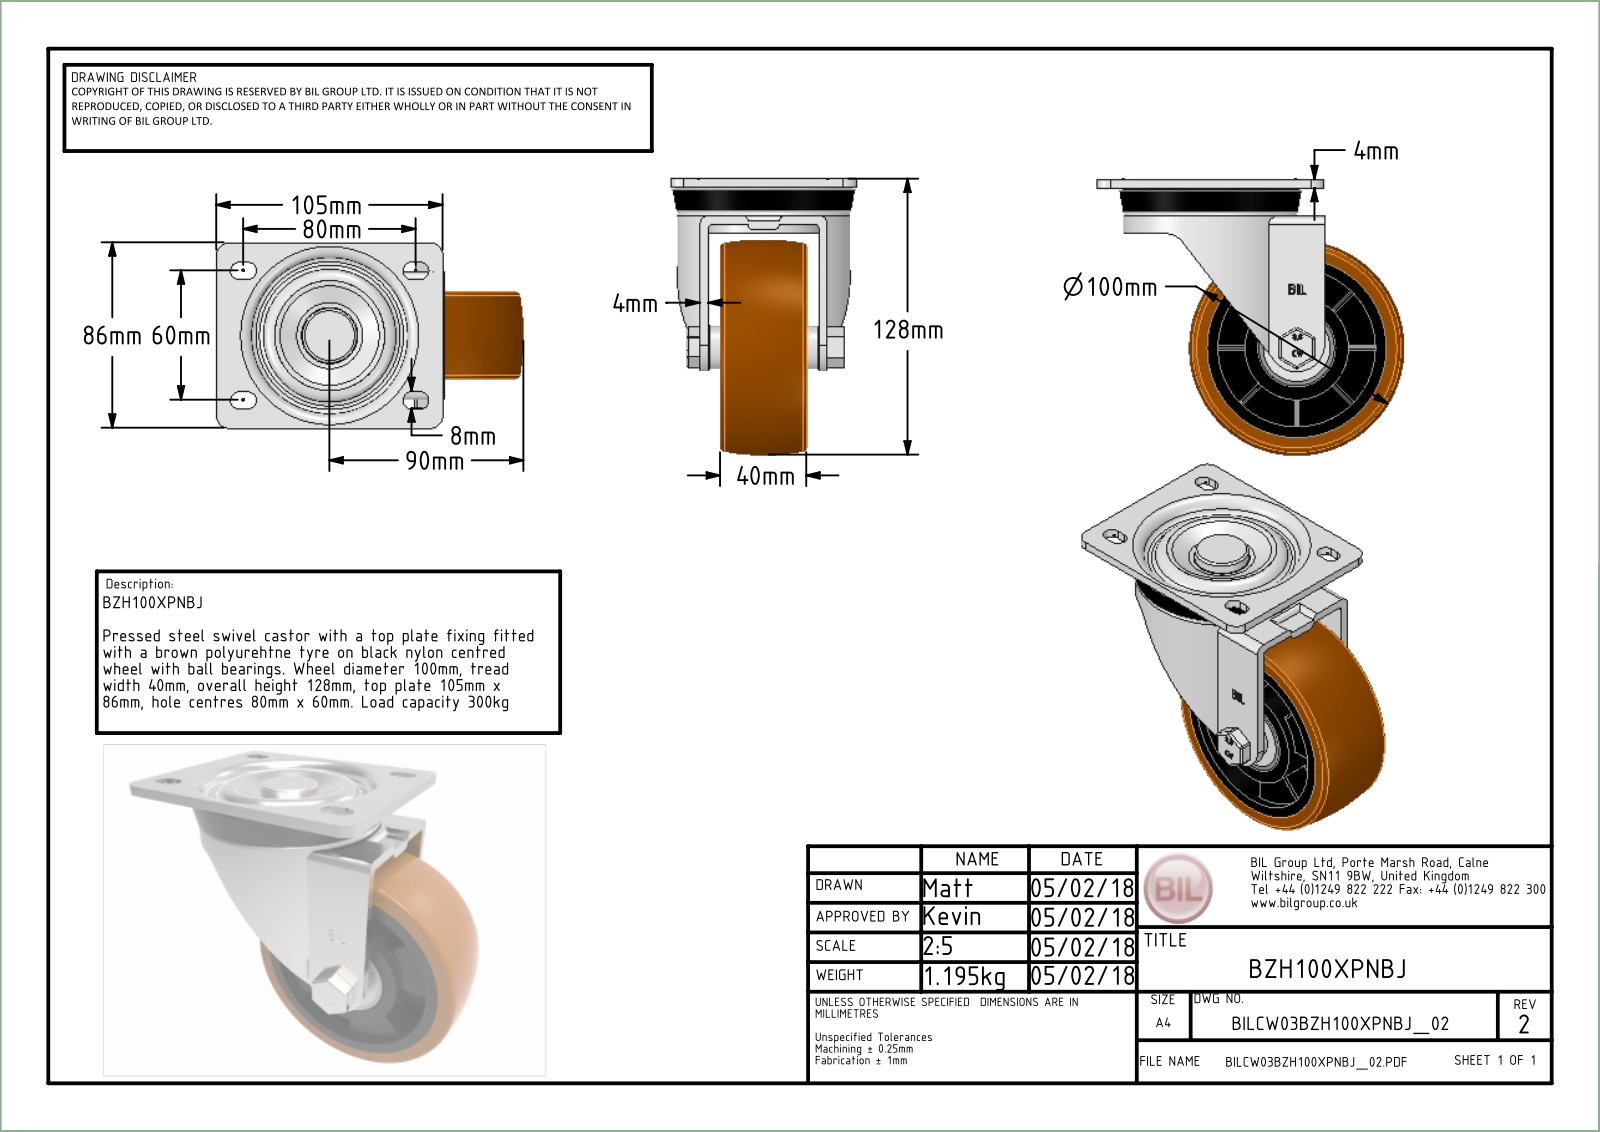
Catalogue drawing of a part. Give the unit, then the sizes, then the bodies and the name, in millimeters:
Units: millimetres
Overall size (bounding box): 142.5 × 128 × 86
Round holes (diameter × count): ⌀32 ×2, ⌀10 ×1, ⌀10.2 ×1, ⌀10.5 ×1, ⌀12 ×1, ⌀15 ×1, ⌀22.5 ×1, ⌀25 ×1, ⌀30 ×1, ⌀31 ×1, ⌀35 ×1, ⌀72 ×1
Round bosses / shafts (diameter × count): ⌀20 ×2, ⌀80 ×1, ⌀50.5 ×1, ⌀48 ×1, ⌀31 ×1, ⌀30.5 ×1, ⌀23 ×1, ⌀22 ×1
Partial cylindrical surfaces — rounded edges, fillets, slot ends (radius × count): R0.5 ×18, R4.5 ×8, R0.75 ×6, R2 ×4, R8 ×4, R4 ×2, R25.41 ×2, R12 ×1
Main face-to-face distances: 4, 5, 9.5, 11.5, 7.5, 5.5, 10.5, 40, 49.5, 55
Volume: 358 014 mm³ · Surface area: 156 679 mm²
Bodies: 37 solids, 1265 faces (457 planar, 205 cylindrical, 603 other)
Part name (STEP PRODUCT): BZH100XPNBJ v4; BZH100AS - 2 v1; ZINC PLATED, PRESSED STEEL TOP PLATE (1); ZINC PLATED, PRESSED STEEL FORKS (1) (+8 more)
STEP written by: Autodesk Translation Framework v14.10.0.0 (AUTOMOTIVE_DESIGN)
